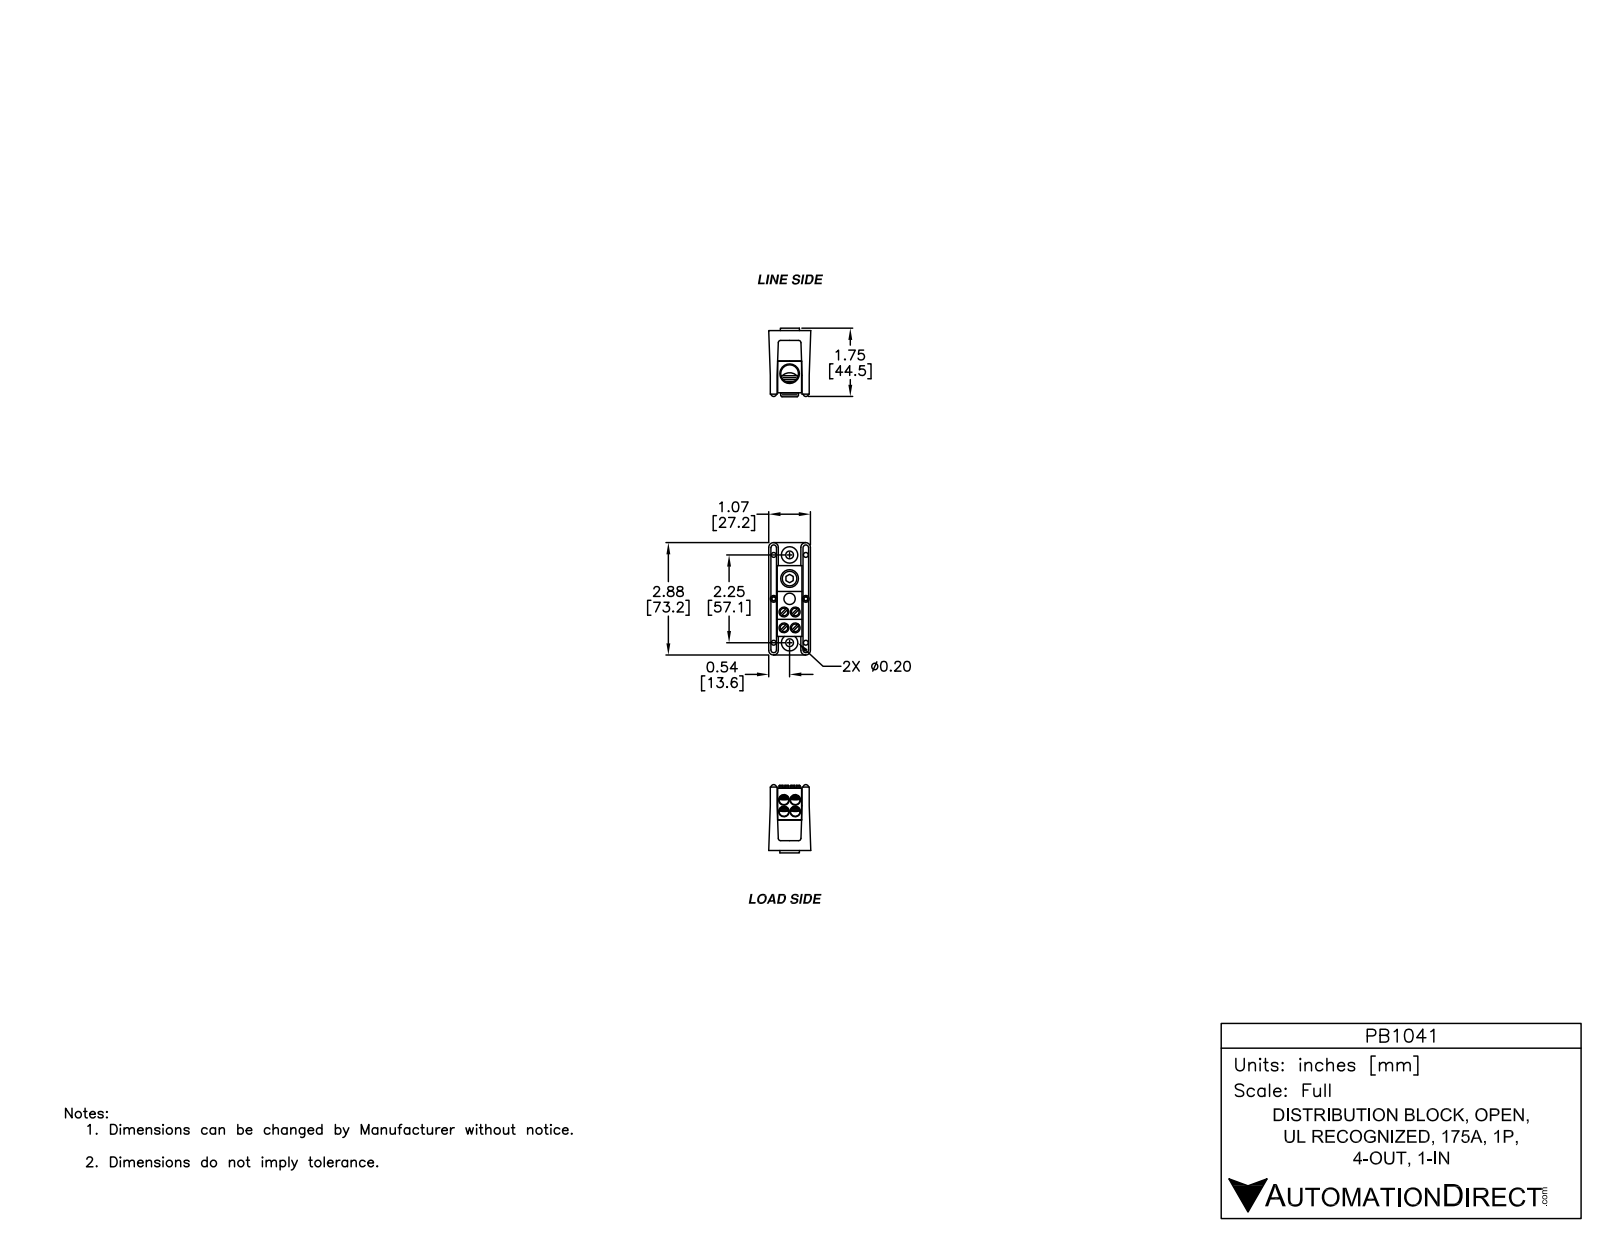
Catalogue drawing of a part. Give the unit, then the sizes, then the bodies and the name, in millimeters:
Units: millimetres
Overall size (bounding box): 72.4 × 46.1 × 25
Round holes (diameter × count): ⌀5.6 ×4, ⌀6.4 ×4, ⌀2.9 ×2, ⌀5.1 ×2, ⌀5.3 ×2, ⌀4.4 ×1, ⌀7.4 ×1, ⌀10 ×1, ⌀11.5 ×1, ⌀12.7 ×1
Round bosses / shafts (diameter × count): ⌀12.7 ×2, ⌀14.8 ×1, ⌀6.4 ×1
Partial cylindrical surfaces — rounded edges, fillets, slot ends (radius × count): R0.6 ×18, R2.1 ×2, R2.2 ×2, R2.3 ×2
Main face-to-face distances: 20.6, 15.6, 16, 3.2, 6.4, 12.9, 3.2, 9.7, 2.2, 17.7
Hole centre spacings: 9.4, 20.1, 4.2, 6.8, 7, 7.1, 7.9, 10.3
Volume: 43 950 mm³ · Surface area: 23 950 mm²
Bodies: 8 solids, 291 faces (130 planar, 113 cylindrical, 48 other)
Part name (STEP PRODUCT): PB1041
STEP written by: SolidWorks 2014 (AUTOMOTIVE_DESIGN)
